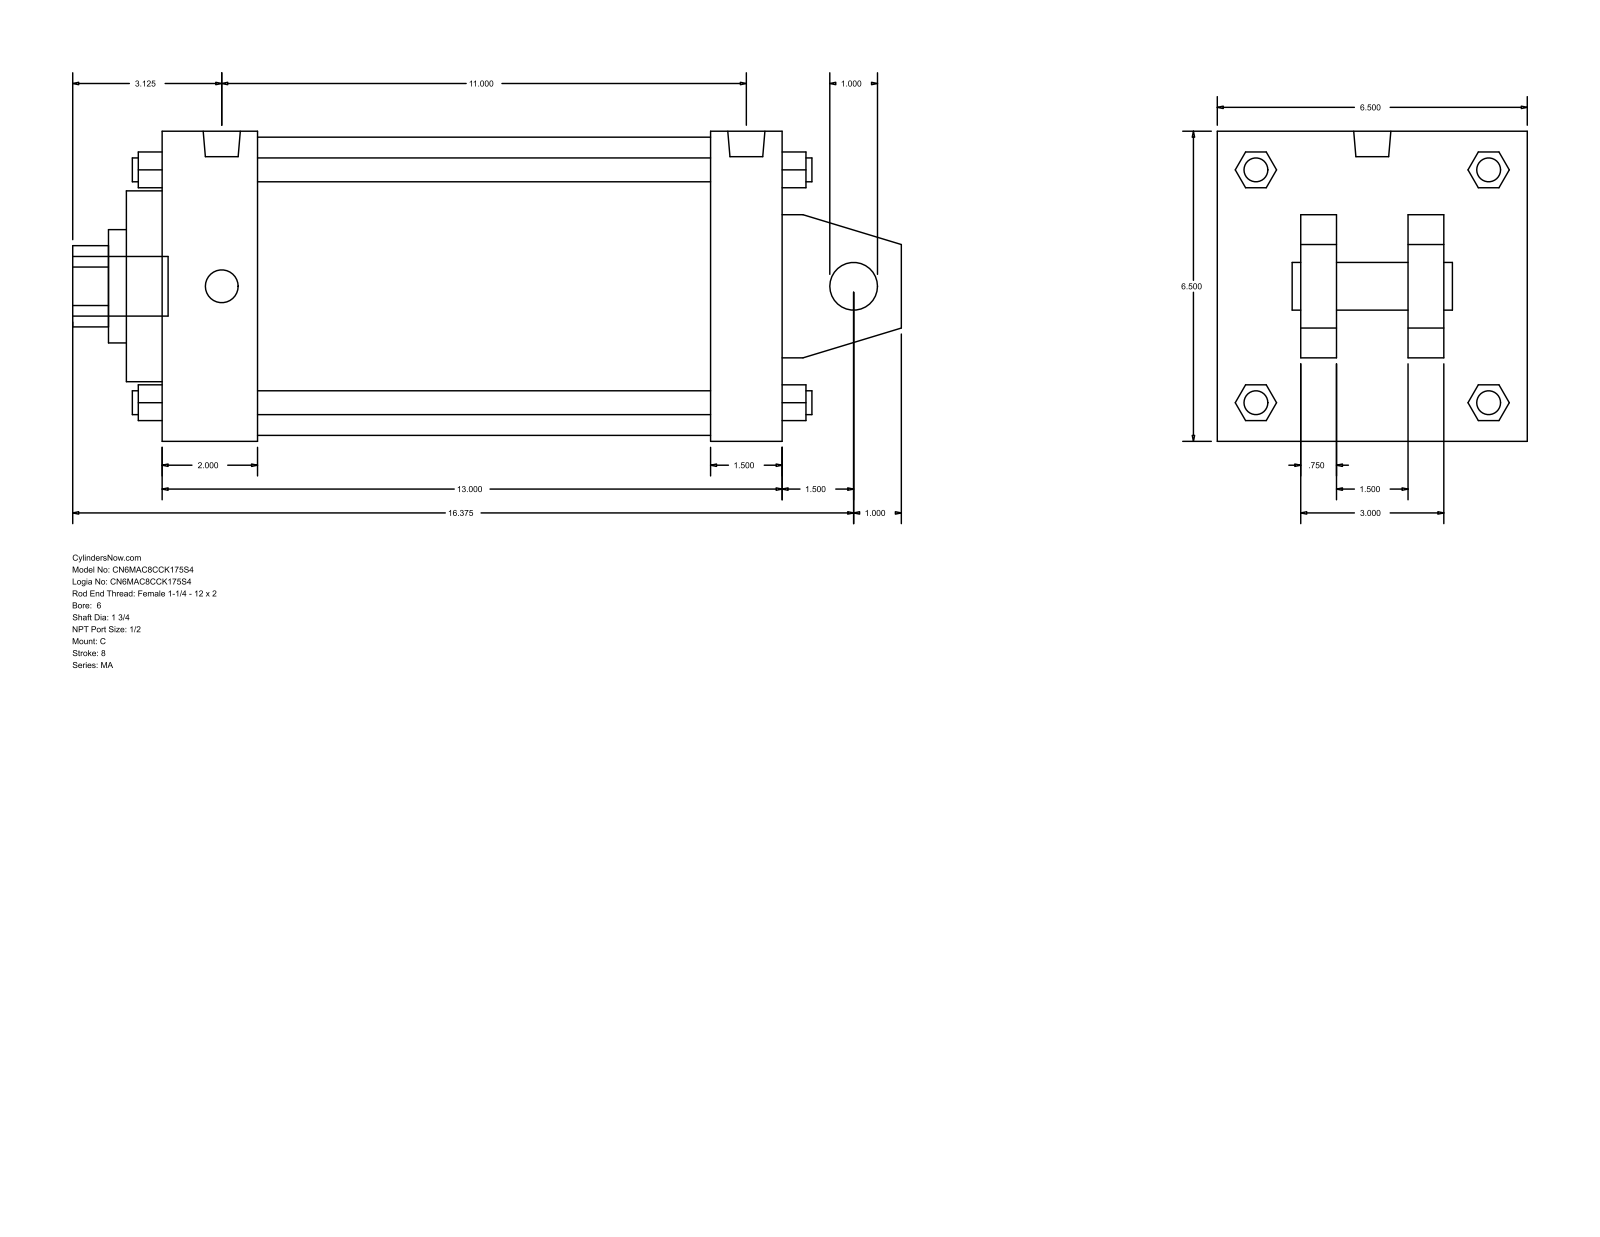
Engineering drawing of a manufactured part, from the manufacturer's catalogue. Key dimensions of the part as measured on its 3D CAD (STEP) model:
Part name (STEP PRODUCT): MA_C__0600_1.75
STEP written by: GSSL Pune (CONFIG_CONTROL_DESIGN)
Units: millimetres
Bodies: 0 solids, 141 faces (109 planar, 32 cylindrical, 0 other)
Overall size (bounding box): 441.32 × 165.1 × 165.1
Round holes (diameter × count): ⌀25.4 ×1, ⌀44.45 ×1, ⌀60.33 ×1, ⌀101.6 ×1, ⌀158.75 ×1
Round bosses / shafts (diameter × count): ⌀17.46 ×4, ⌀12.7 ×4, ⌀19.77 ×2, ⌀31.75 ×1
Partial cylindrical surfaces — rounded edges, fillets, slot ends (radius × count): R21.63 ×1
Main face-to-face distances: 165.1, 330.2, 19.05, 63.5, 101.6, 50.8, 120.65, 44.45, 57.15, 279.4
